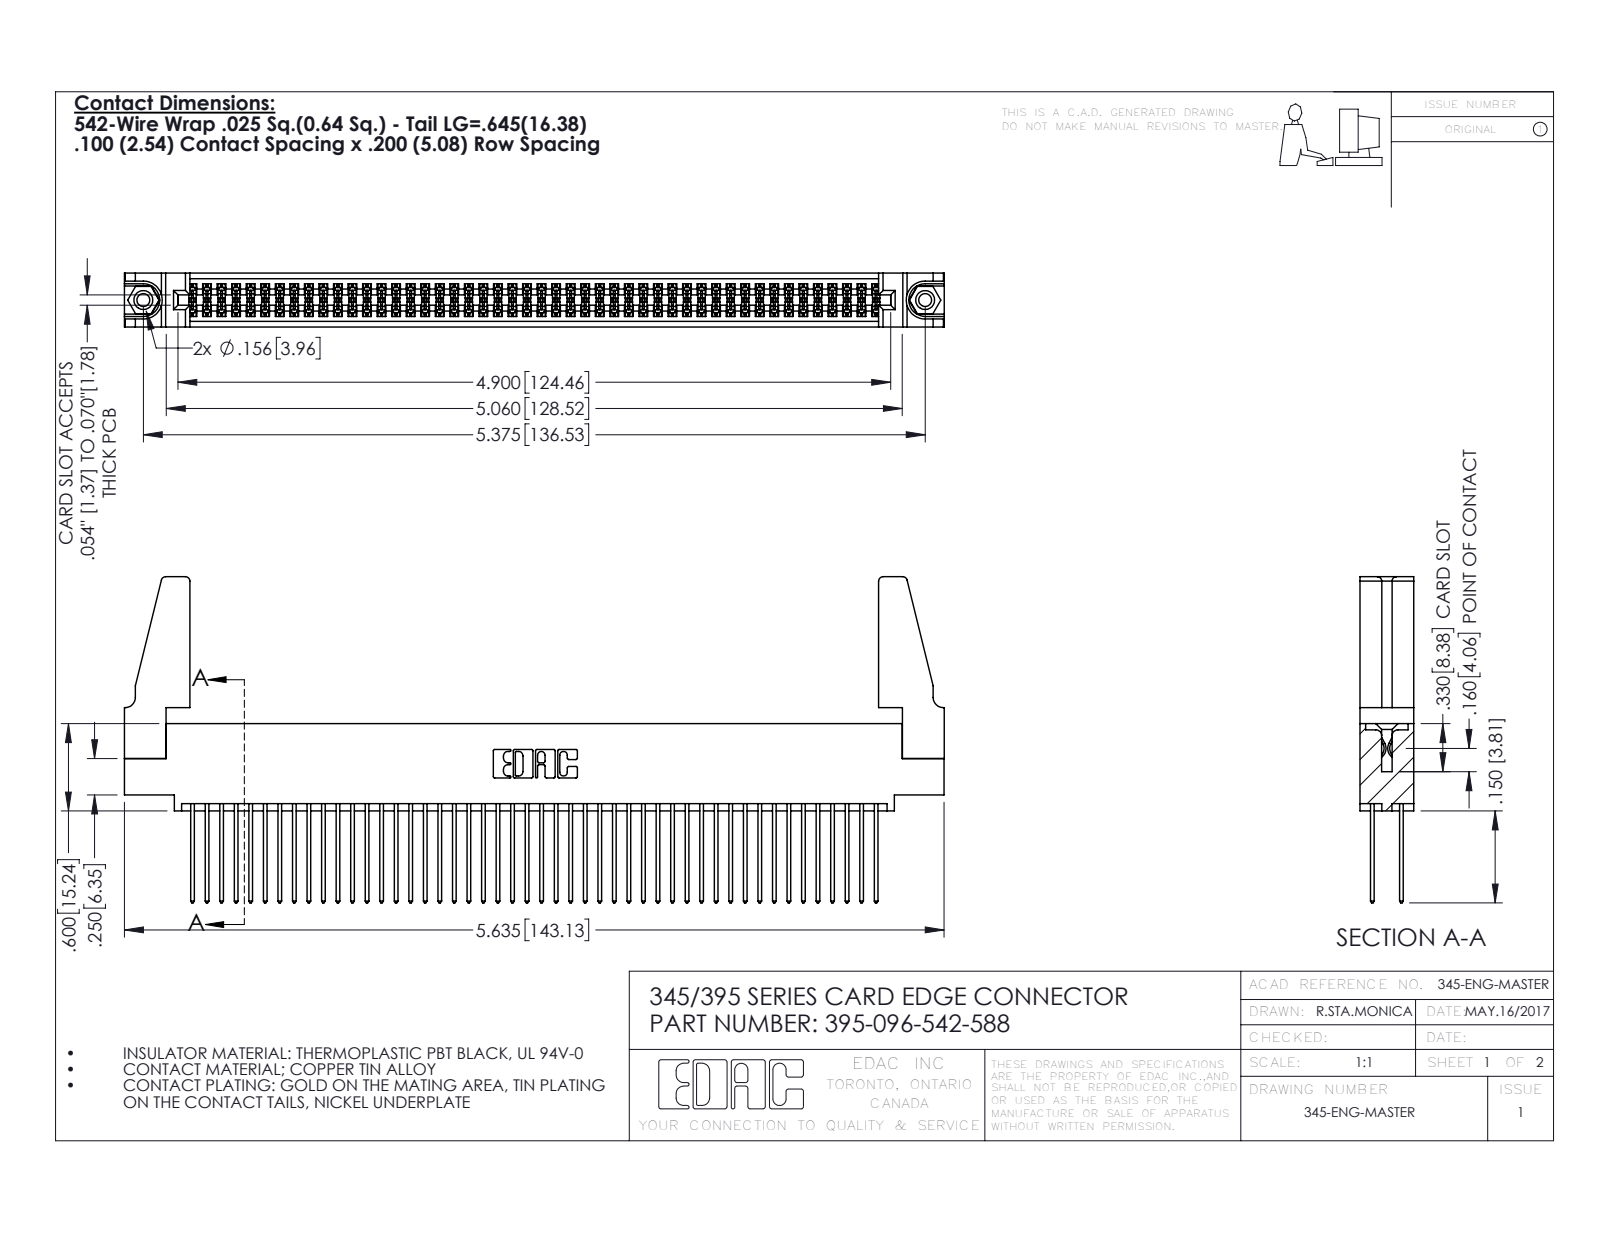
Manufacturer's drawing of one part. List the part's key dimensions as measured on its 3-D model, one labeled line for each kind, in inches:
Part name (STEP PRODUCT): 345-250-001_345-250-001-102; 345-220-078_345-220-088; 395-096-542-588; 345 Part_0.110 Offset - 0.156 Dia-TH (+1 more)
STEP written by: SolidWorks 2016 (CONFIG_CONTROL_DESIGN)
Units: inches
Bodies: 101 solids, 5054 faces (3324 planar, 1714 cylindrical, 16 other)
Overall size (bounding box): 5.636 × 2.242 × 0.37
Volume: 1.073 in³ · Surface area: 41.25 in²
Round holes (diameter × count): ⌀0.089 ×2, ⌀0.125 ×2, ⌀0.156 ×2, ⌀0.064 ×1
Round bosses / shafts (diameter × count): ⌀0.155 ×2
Partial cylindrical surfaces — rounded edges, fillets, slot ends (radius × count): R0.006 ×144, R0.01 ×96, R0.01 ×22, R0.03 ×8, R0.007 ×6, R0.031 ×6, R0.026 ×3, R0.014 ×2
Main face-to-face distances: 0.072, 0.298, 0.2, 0.098, 0.272, 0.025, 0.37, 0.225, 0.175, 0.149
Hole centre spacings: 0.27, 5.139, 5.375
